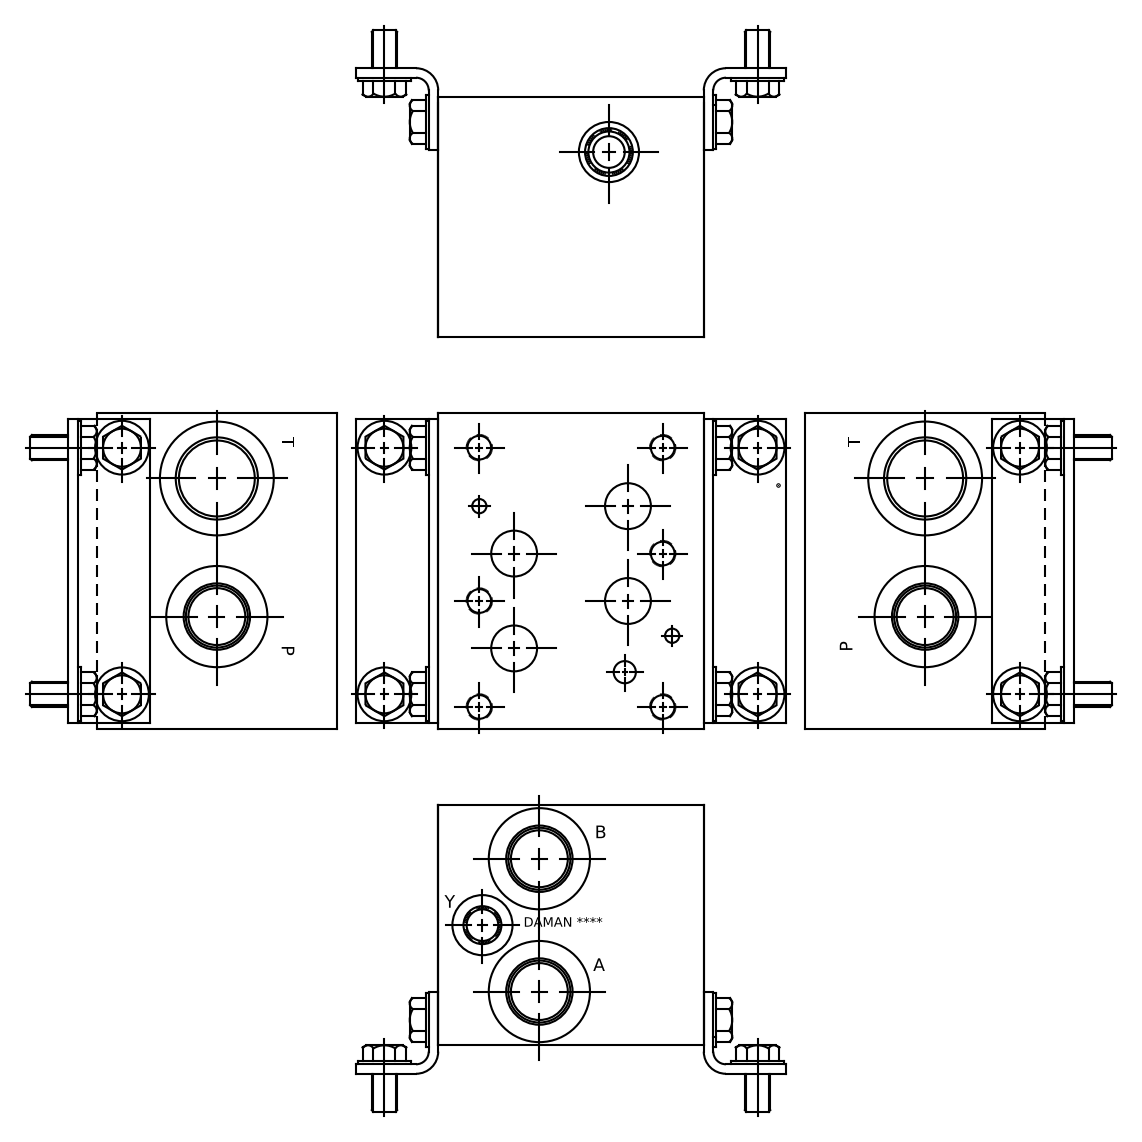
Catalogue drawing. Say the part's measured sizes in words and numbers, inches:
The part is named "Part_AD08P015S~1C_3D". Its 3-D file was written by "Autodesk Inventor 2020 (AUTOMOTIVE_DESIGN)". It is 1 solid with 588 faces: 321 planar, 70 cylindrical and 197 other. Overall it measures 6.25 by 5.25 by 4.75 inches. Its volume is 138 cubic inches and its surface area 241.4 square inches. Round holes: 8 of diameter 0.422, 8 of diameter 0.5, 3 of diameter 0.906, 3 of diameter 1.231, 3 of diameter 1.329, 3 of diameter 1.934, 2 of diameter 0.281, 2 of diameter 1.125, 2 of diameter 1.313, 2 of diameter 1.313, 2 of diameter 1.398, 1 of diameter 0.437. The main face-to-face distances are 4.75, 5.25, 6.25, 0.031, 5.219, 6.219, 5.188, 0.781, 0.75, 4.469. The hole center spacings are 1.163, 1.163, 1.875, 2.094, 2.438, 2.938, 3.607, 4.221.
